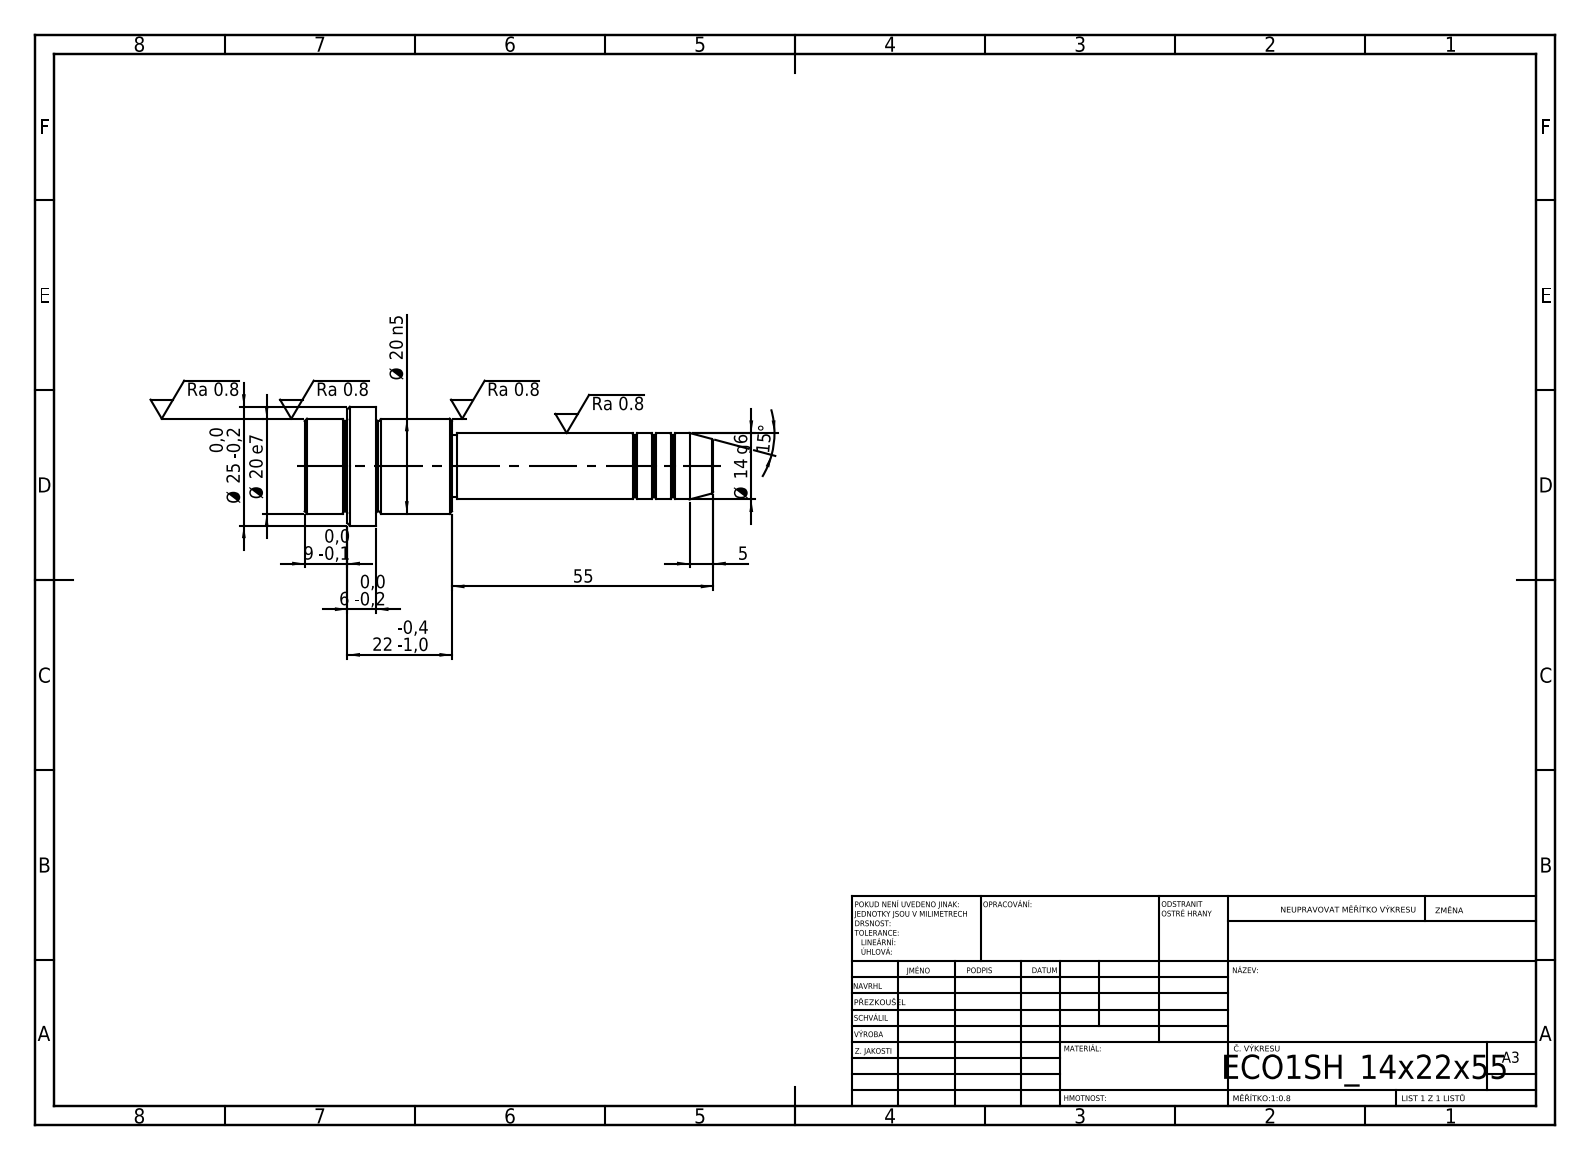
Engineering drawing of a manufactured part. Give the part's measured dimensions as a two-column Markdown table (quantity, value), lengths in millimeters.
| quantity | value |
| --- | --- |
| STEP written by | SolidWorks 2019 (CONFIG_CONTROL_DESIGN) |
| units | millimeters |
| bodies | 1 solid, 52 faces (6 planar, 16 cylindrical, 30 other) |
| overall size | 86 × 25 × 25 |
| volume | 18 982 mm³ |
| surface area | 5 481 mm² |
| round bosses / shafts (diameter × count) | 25 × 1, 20 × 1, 14 × 1, 13 × 1 |
| main face-to-face distances | 15, 16, 31, 22, 6, 9, 55, 71, 77, 86 |
